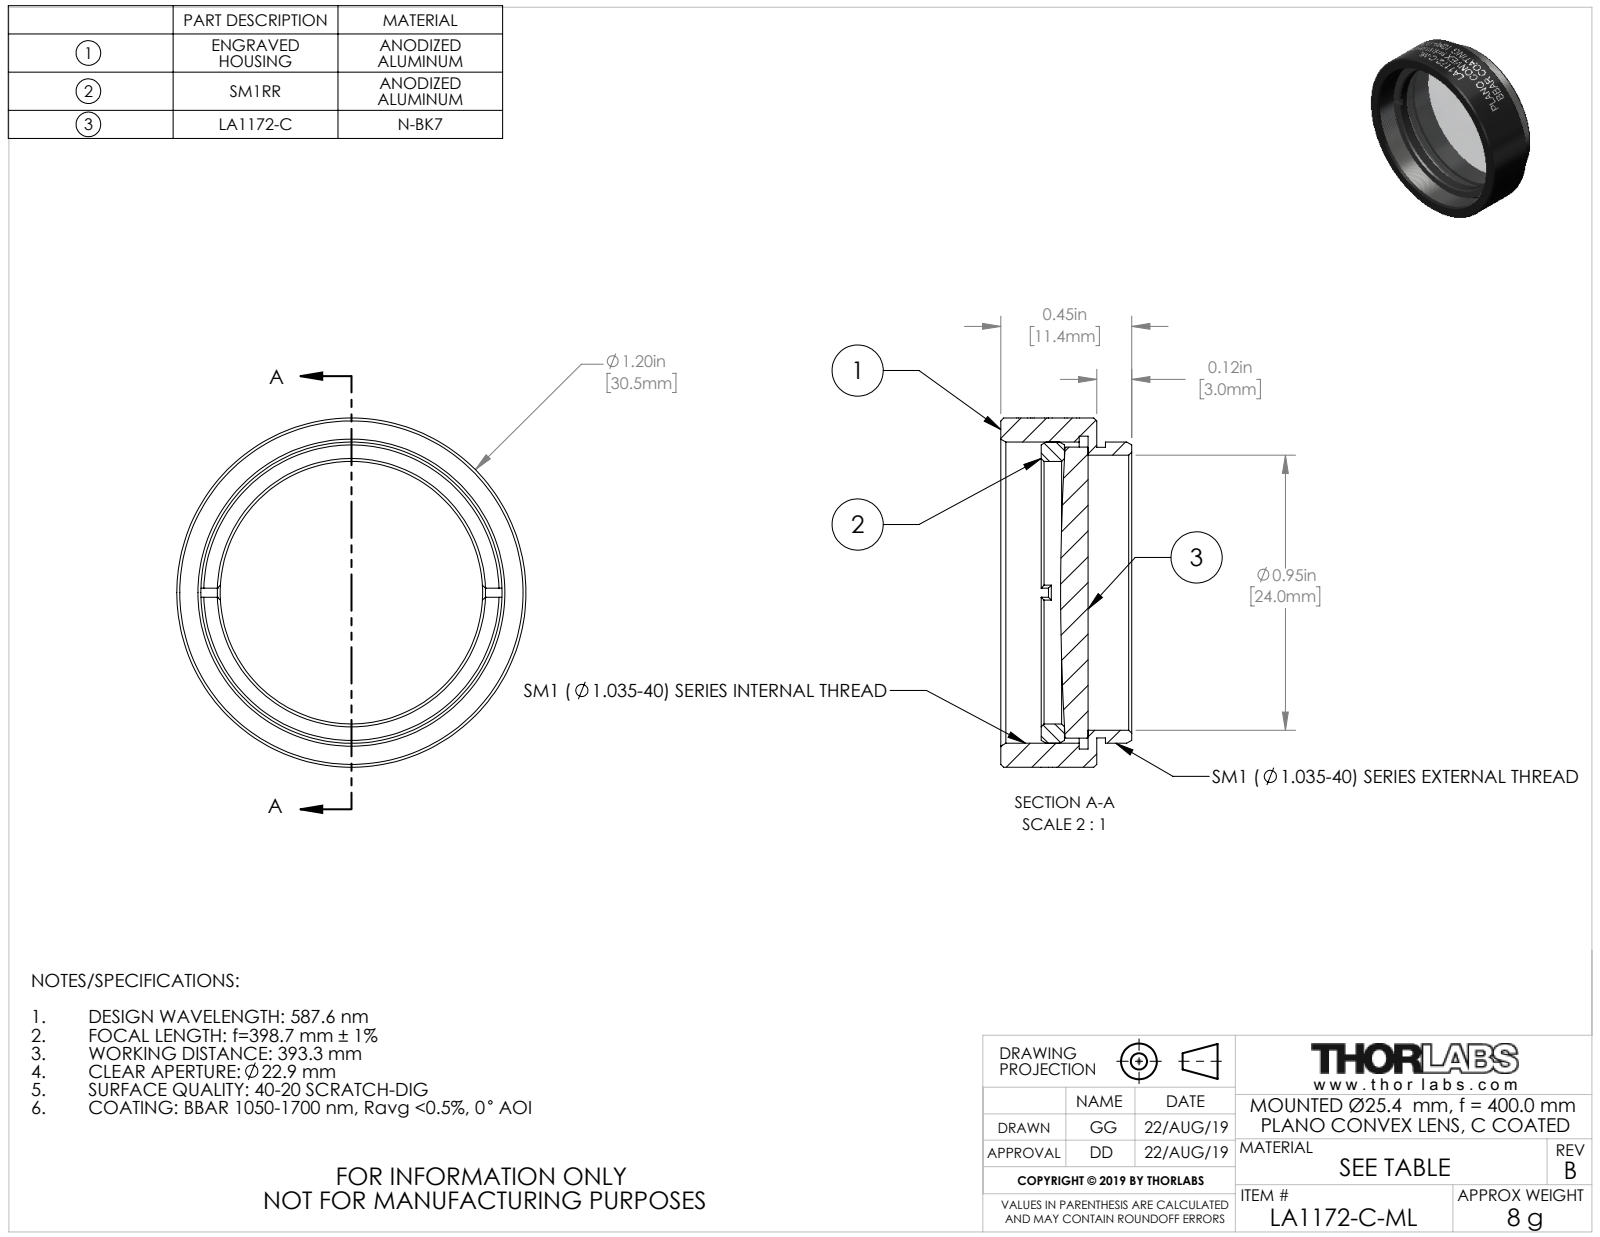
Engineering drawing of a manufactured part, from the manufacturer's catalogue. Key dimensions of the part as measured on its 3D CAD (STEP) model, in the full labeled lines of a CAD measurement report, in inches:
Part name (STEP PRODUCT): 24449-E0W
STEP written by: SolidWorks 2018 (CONFIG_CONTROL_DESIGN)
Units: inches
Bodies: 3 solids, 158 faces (20 planar, 110 cylindrical, 28 other)
Overall size (bounding box): 1.2 × 1.2 × 0.45
Volume: 0.195 in³ · Surface area: 6.676 in²
Round holes (diameter × count): ⌀0.902 ×1, ⌀0.945 ×1, ⌀1.035 ×1, ⌀1.075 ×1
Round bosses / shafts (diameter × count): ⌀1.2 ×1, ⌀1.035 ×1, ⌀1 ×1, ⌀0.999 ×1
Main face-to-face distances: 0.03, 0.33, 0.3, 0.111, 0.081, 0.219, 0.191, 0.161, 0.08, 0.139
